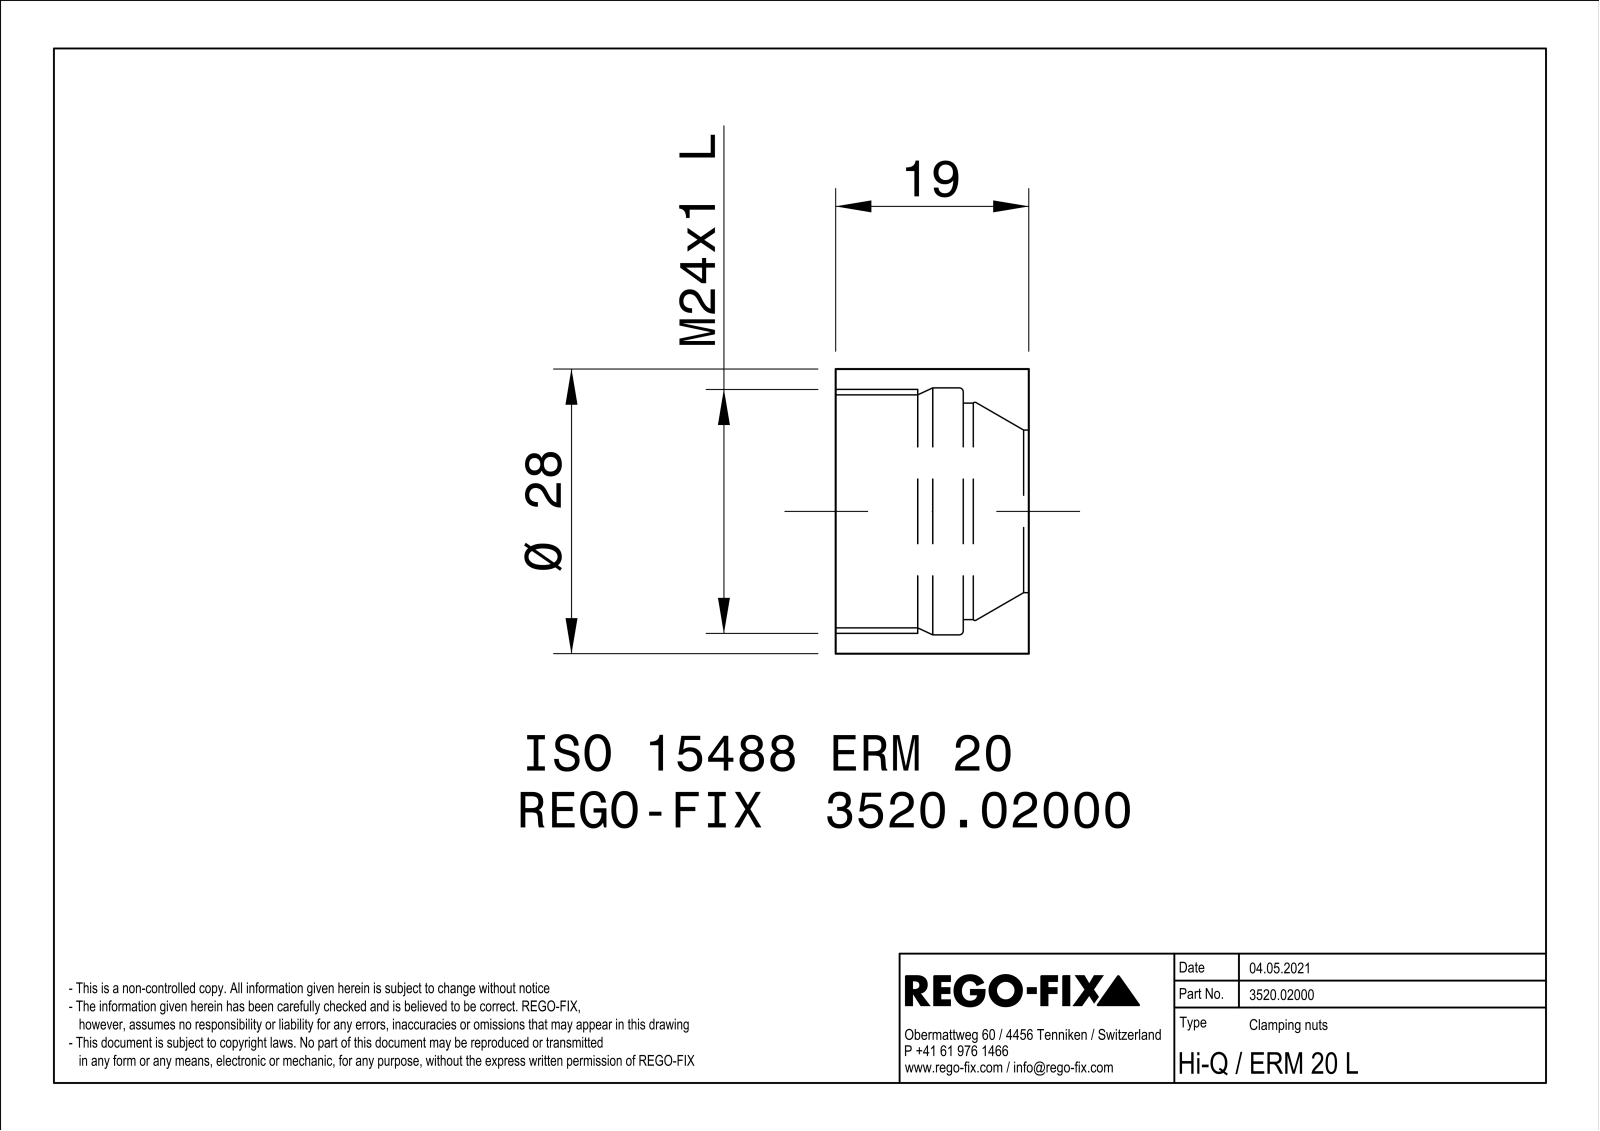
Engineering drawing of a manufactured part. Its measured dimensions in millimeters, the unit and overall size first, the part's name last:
Units: millimetres
Overall size (bounding box): 28 × 28 × 19
Round holes (diameter × count): ⌀16 ×1, ⌀21.3 ×1, ⌀22.92 ×1, ⌀24.3 ×1
Round bosses / shafts (diameter × count): ⌀28 ×1
Main face-to-face distances: 19, 6.45, 12.55, 5
Volume: 4 166 mm³ · Surface area: 3 744 mm²
Bodies: 1 solid, 41 faces (21 planar, 6 cylindrical, 14 other)
Part name (STEP PRODUCT): NOCUT
STEP written by: SIEMENS PLM Software Solid Edge ST10 (AUTOMOTIVE_DESIGN)
